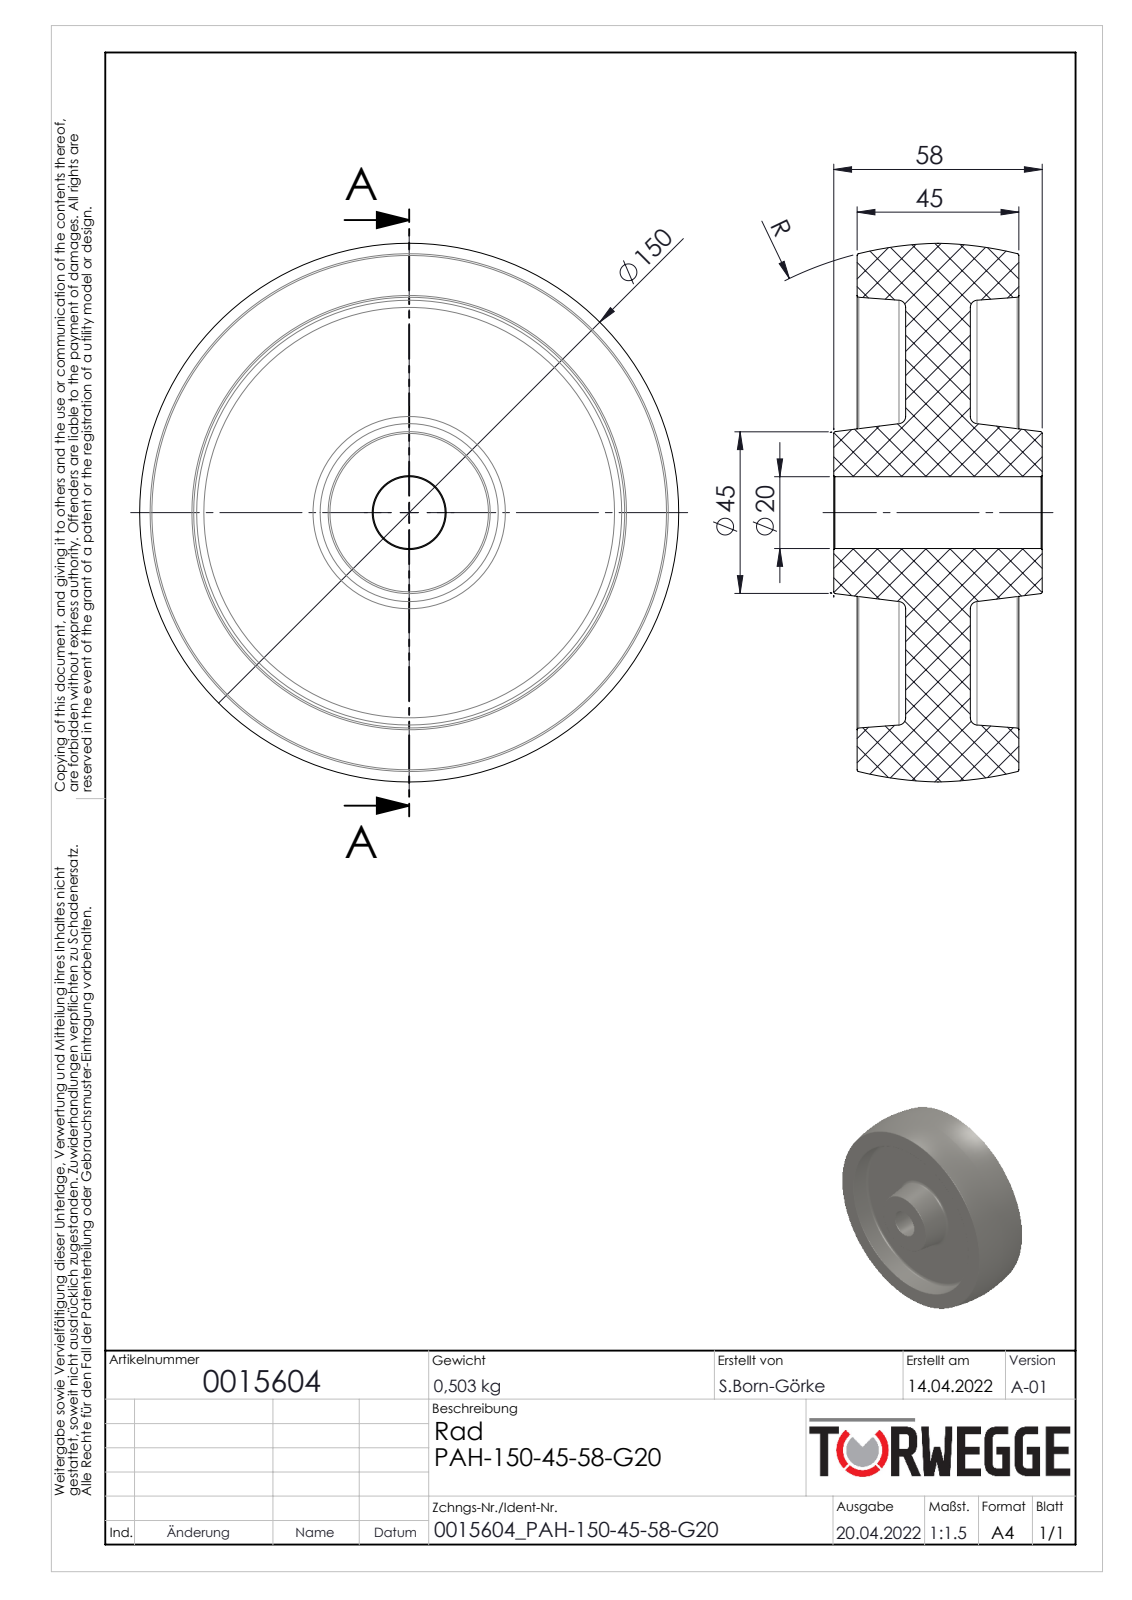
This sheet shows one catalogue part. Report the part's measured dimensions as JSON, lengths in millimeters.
{"part_name": "0015604", "step_written_by": "SolidWorks 2020 (AUTOMOTIVE_DESIGN)", "units": "millimeters", "bodies": {"solids": 1, "faces": 44, "planar": 6, "cylindrical": 2, "other": 36}, "overall_size": [150, 150, 58], "volume_mm3": 525981, "surface_area_mm2": 70319, "round_holes": [[20, 1]], "face_to_face_distances": [13.5, 31.5, 18, 45, 6.5, 20, 38, 51.5, 58]}
